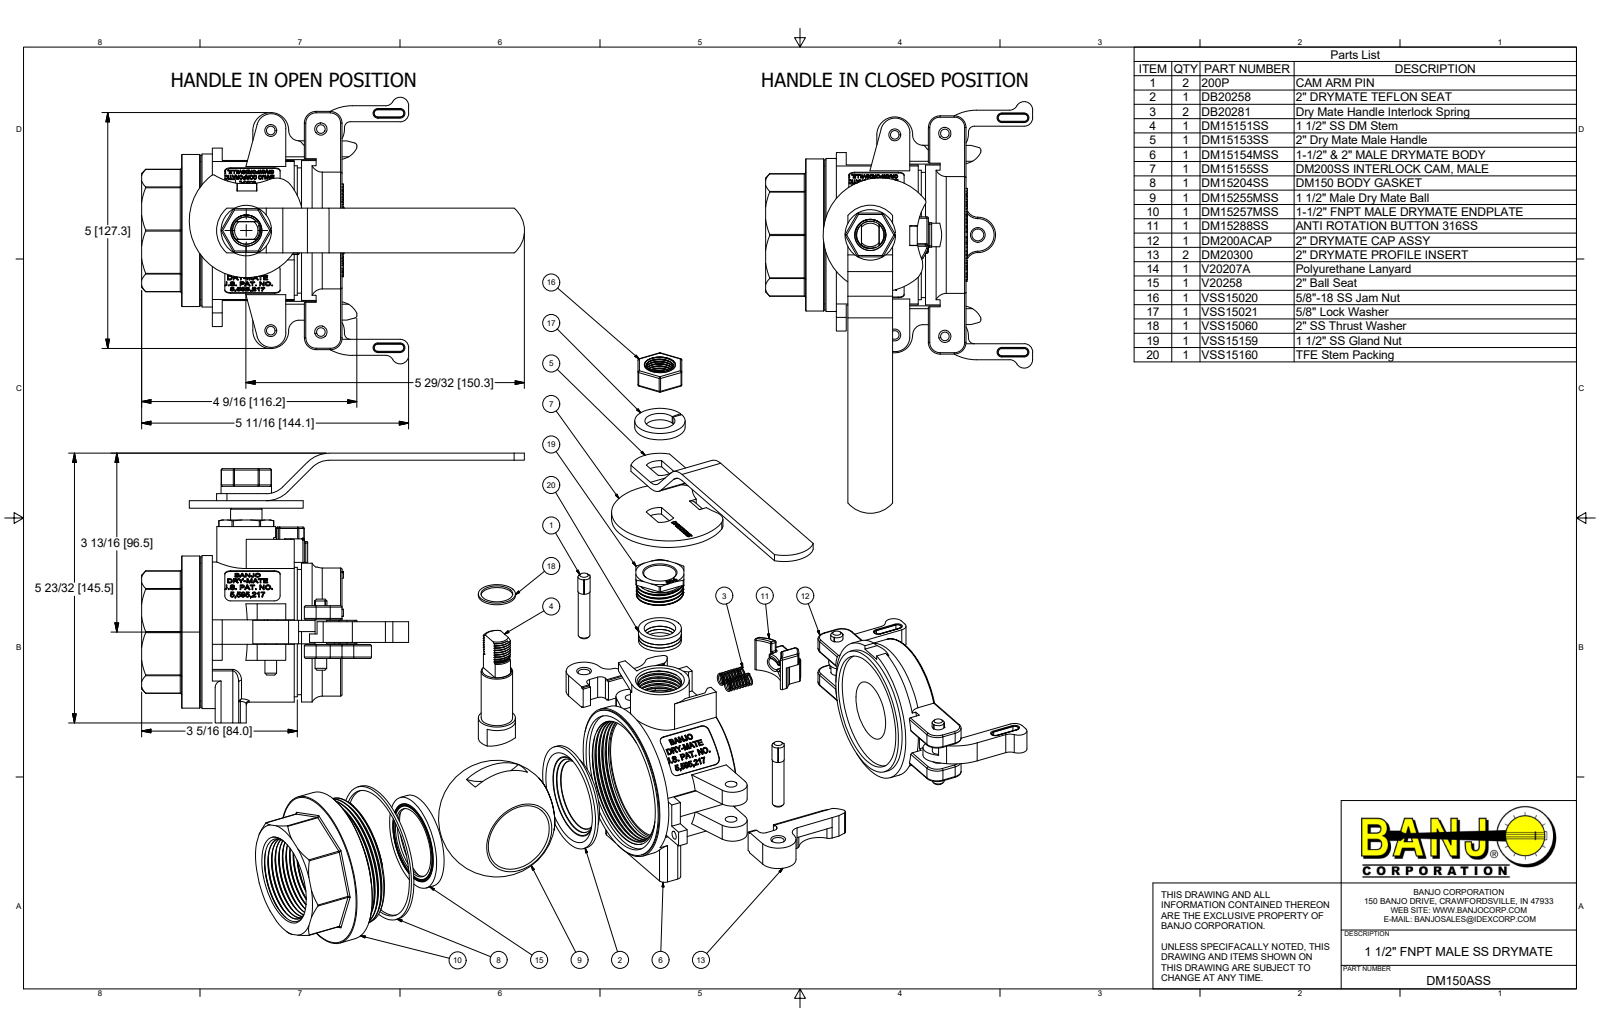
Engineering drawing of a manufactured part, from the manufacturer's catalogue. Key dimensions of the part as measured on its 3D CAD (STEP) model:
Part name (STEP PRODUCT): DM150ASS; DM15154MSS; DB20258; DB20281 (+8 more)
STEP written by: Autodesk Inventor 2017 (AUTOMOTIVE_DESIGN)
Units: millimetres
Bodies: 32 solids, 2553 faces (1131 planar, 464 cylindrical, 958 other)
Overall size (bounding box): 222 × 145.54 × 144.07
Volume: 426 817 mm³ · Surface area: 187 049 mm²
Round holes (diameter × count): ⌀6.35 ×5, ⌀6.5 ×4, ⌀3.17 ×3, ⌀38.1 ×2, ⌀4.57 ×1, ⌀14.73 ×1, ⌀16.26 ×1, ⌀16.82 ×1, ⌀17.02 ×1, ⌀17.17 ×1, ⌀17.53 ×1, ⌀21.34 ×1
Round bosses / shafts (diameter × count): ⌀6.6 ×4, ⌀6.32 ×4, ⌀7.11 ×3, ⌀82.04 ×1, ⌀81.03 ×1, ⌀75.56 ×1, ⌀75.44 ×1, ⌀74.8 ×1
Partial cylindrical surfaces — rounded edges, fillets, slot ends (radius × count): R0.76 ×96, R1.52 ×8, R3.17 ×8, R4.57 ×6, R6.35 ×6, R0.64 ×4, R1.91 ×4, R3.05 ×4
Main face-to-face distances: 7.57, 21.84, 7.87, 21.59, 3.81, 29.72, 2.28, 20.87, 4.07, 25.91
Hole centre spacings: 24.13, 41.8, 1.22, 27.06, 28.28, 55.56, 57.19, 57.56
